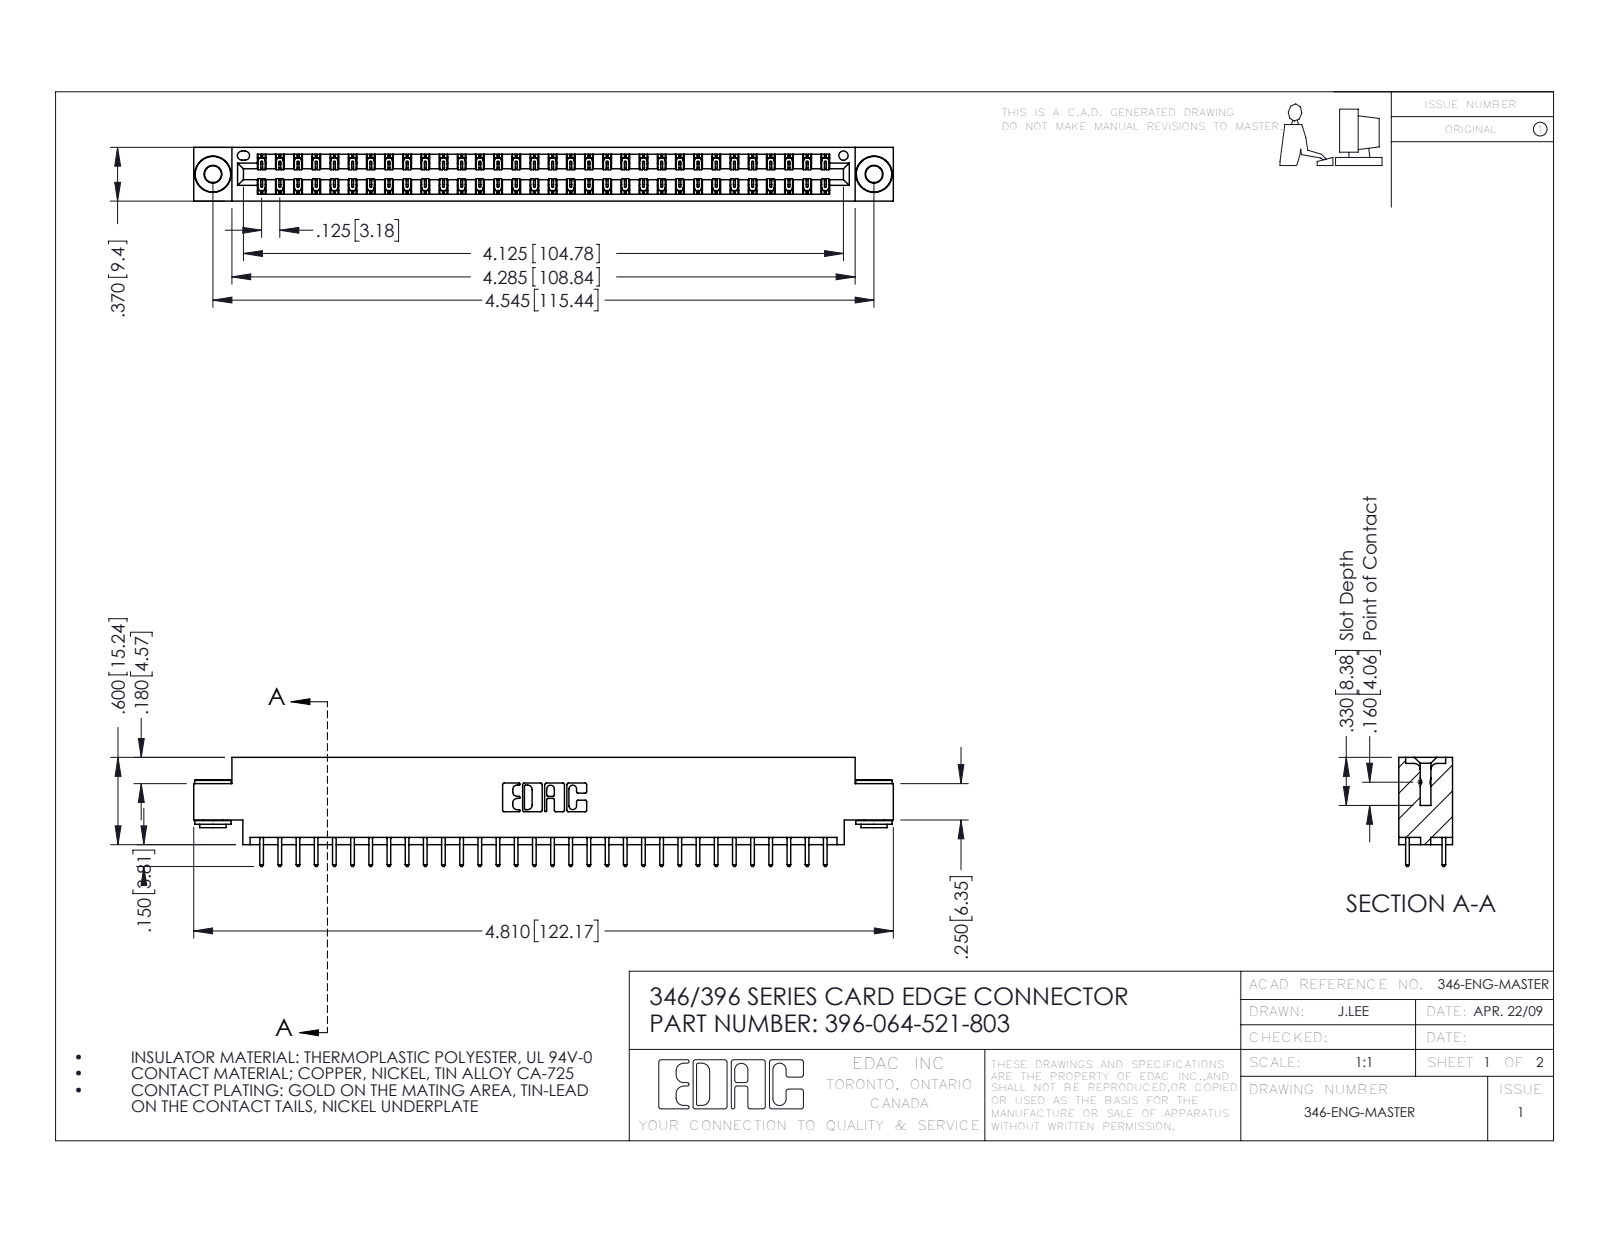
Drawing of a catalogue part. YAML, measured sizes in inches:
part_name: "345-292-001_345-293-121; 346 Part_0.170 Offset - 0.156 Dia-TH; 345-250-002_345-250-002-102; 396-064-521-803"
step_written_by: "SolidWorks 2016 (CONFIG_CONTROL_DESIGN)"
units: inches
bodies: {solids: 67, faces: 3492, planar: 2330, cylindrical: 1154, other: 8}
overall_size: [4.81, 0.75, 0.37]
volume: 0.712
surface_area: 24.97
round_holes:
  - {diameter: 0.116, count: 2}
  - {diameter: 0.156, count: 2}
  - {diameter: 0.064, count: 1}
round_bosses_or_shafts:
  - {diameter: 0.25, count: 2}
  - {diameter: 0.18, count: 2}
  - {diameter: 0.136, count: 2}
partial_cylinders:
  - {radius: 0.006, count: 96}
  - {radius: 0.01, count: 64}
  - {radius: 0.01, count: 22}
  - {radius: 0.007, count: 6}
  - {radius: 0.031, count: 6}
  - {radius: 0.026, count: 3}
  - {radius: 0.014, count: 2}
  - {radius: 0.022, count: 2}
face_to_face_distances: [0.048, 0.322, 0.37, 0.25, 0.025, 0.072, 0.298, 0.275, 0.148, 0.222]
hole_center_spacings: [0.246, 4.337, 4.545]
